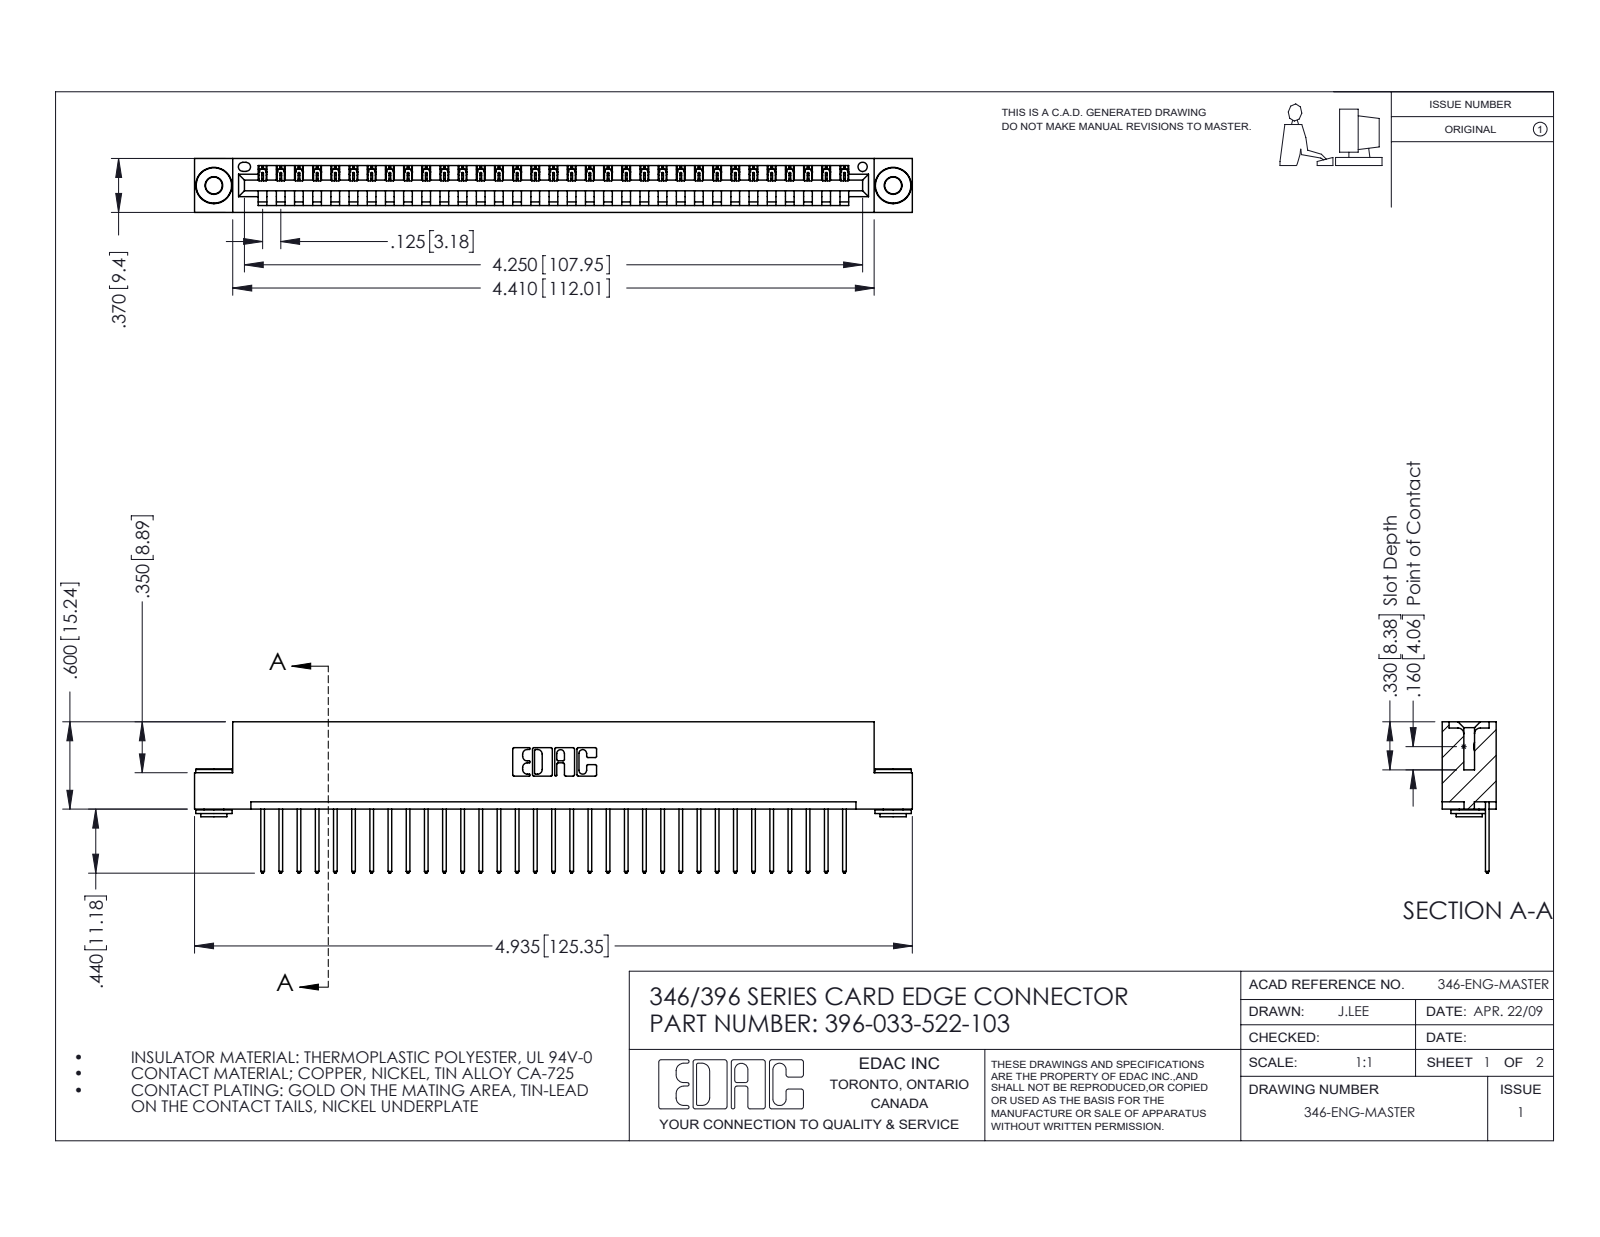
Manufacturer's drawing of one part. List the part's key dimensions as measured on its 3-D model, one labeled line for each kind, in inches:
Part name (STEP PRODUCT): 396-033-522-103; 345-250-002_345-250-002-102; 346 Part_Flush Mounting Lugs - 0.156 Dia-TH; 345-292-001_345-293-122
STEP written by: SolidWorks 2016 (CONFIG_CONTROL_DESIGN)
Units: inches
Bodies: 36 solids, 2074 faces (1406 planar, 660 cylindrical, 8 other)
Overall size (bounding box): 4.935 × 1.04 × 0.37
Volume: 0.73 in³ · Surface area: 23.55 in²
Round holes (diameter × count): ⌀0.116 ×2, ⌀0.156 ×2, ⌀0.064 ×1
Round bosses / shafts (diameter × count): ⌀0.25 ×2, ⌀0.18 ×2, ⌀0.136 ×2
Partial cylindrical surfaces — rounded edges, fillets, slot ends (radius × count): R0.006 ×66, R0.01 ×66, R0.01 ×22, R0.007 ×6, R0.031 ×6, R0.026 ×3, R0.031 ×2, R0.04 ×2
Main face-to-face distances: 0.048, 0.322, 0.37, 0.25, 0.025, 0.072, 0.298, 0.148, 0.222, 0.1
Hole centre spacings: 0.246, 4.462, 4.67
